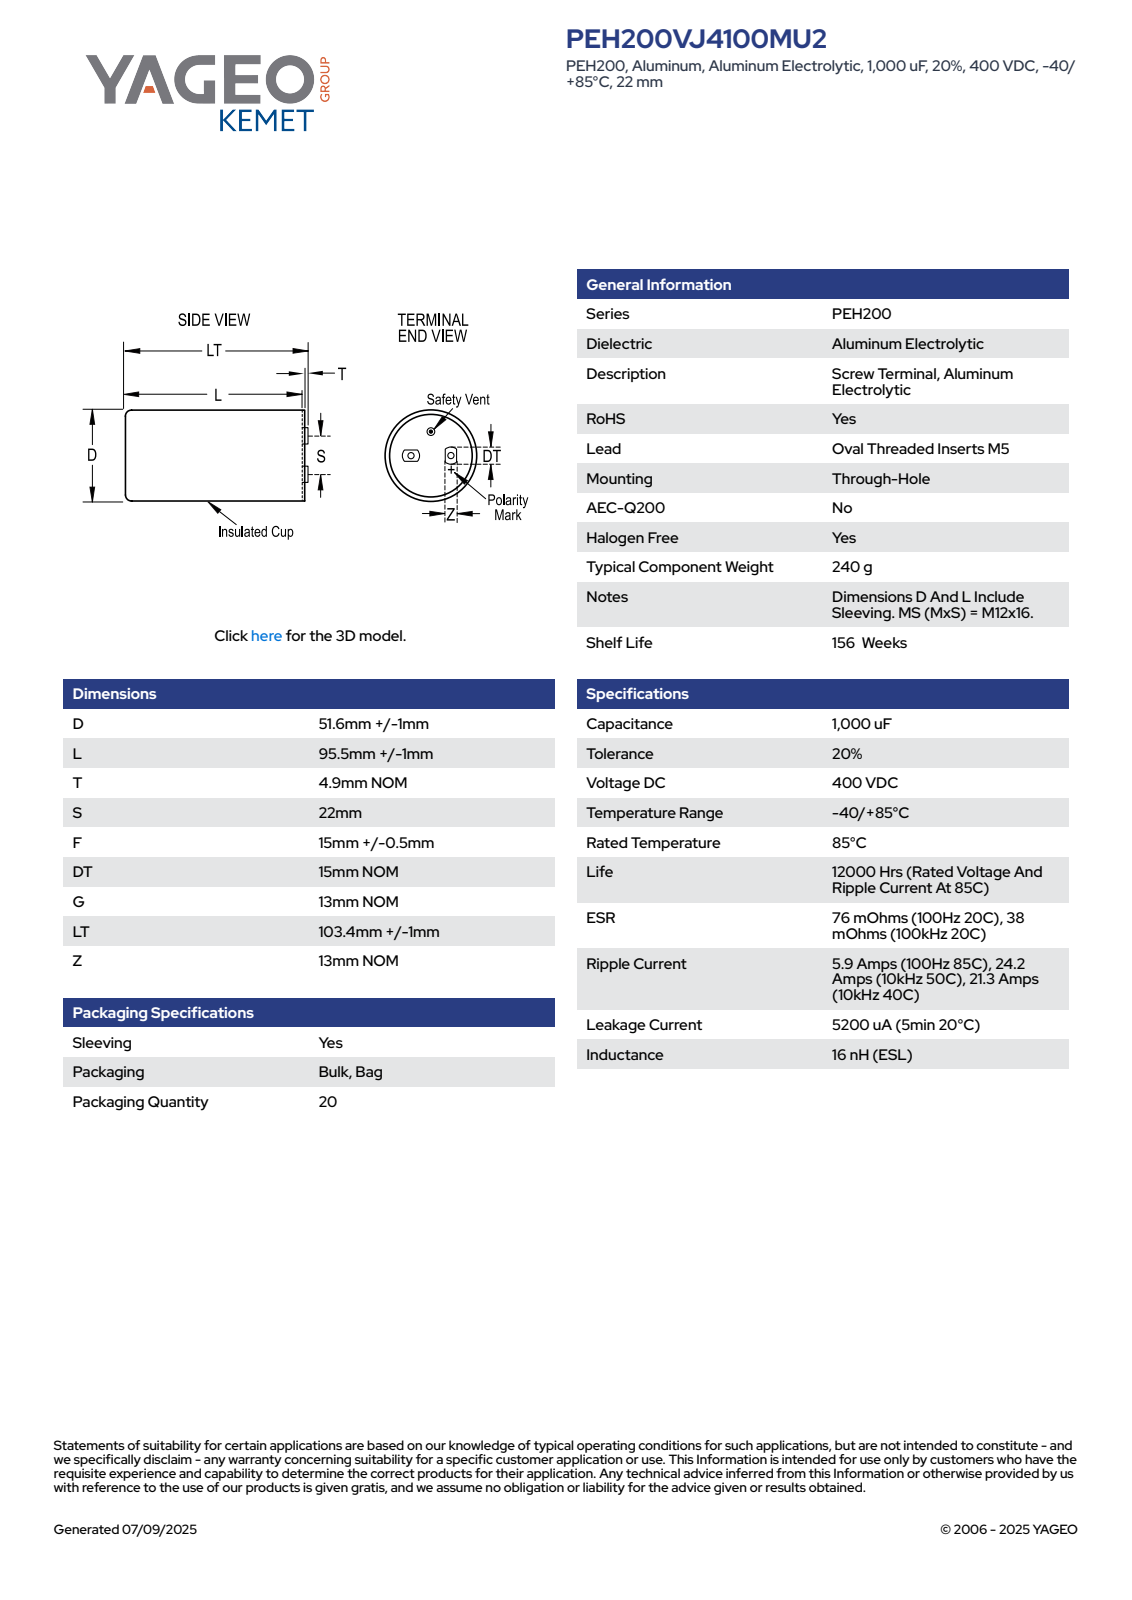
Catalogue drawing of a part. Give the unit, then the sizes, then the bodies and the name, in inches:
Units: inches
Overall size (bounding box): 4.11 × 2.071 × 2.071
Round holes (diameter × count): ⌀0.158 ×2, ⌀1.992 ×1
Round bosses / shafts (diameter × count): ⌀0.295 ×2, ⌀2.071 ×1
Partial cylindrical surfaces — rounded edges, fillets, slot ends (radius × count): R0.295 ×2, R1.035 ×1
Main face-to-face distances: 3.799, 0.311, 4.11, 0.193, 0.118, 3.917, 0.512, 0.508, 0.315, 0.197
Hole centre spacings: 0.433, 0.866
Volume: 12.97 in³ · Surface area: 35.4 in²
Bodies: 3 solids, 91 faces (38 planar, 21 cylindrical, 32 other)
Part name (STEP PRODUCT): Oval_Terminal_2; CARC_D52.6L96.5S22T4.9; Can_2
STEP written by: SolidWorks 2014 (AUTOMOTIVE_DESIGN)
